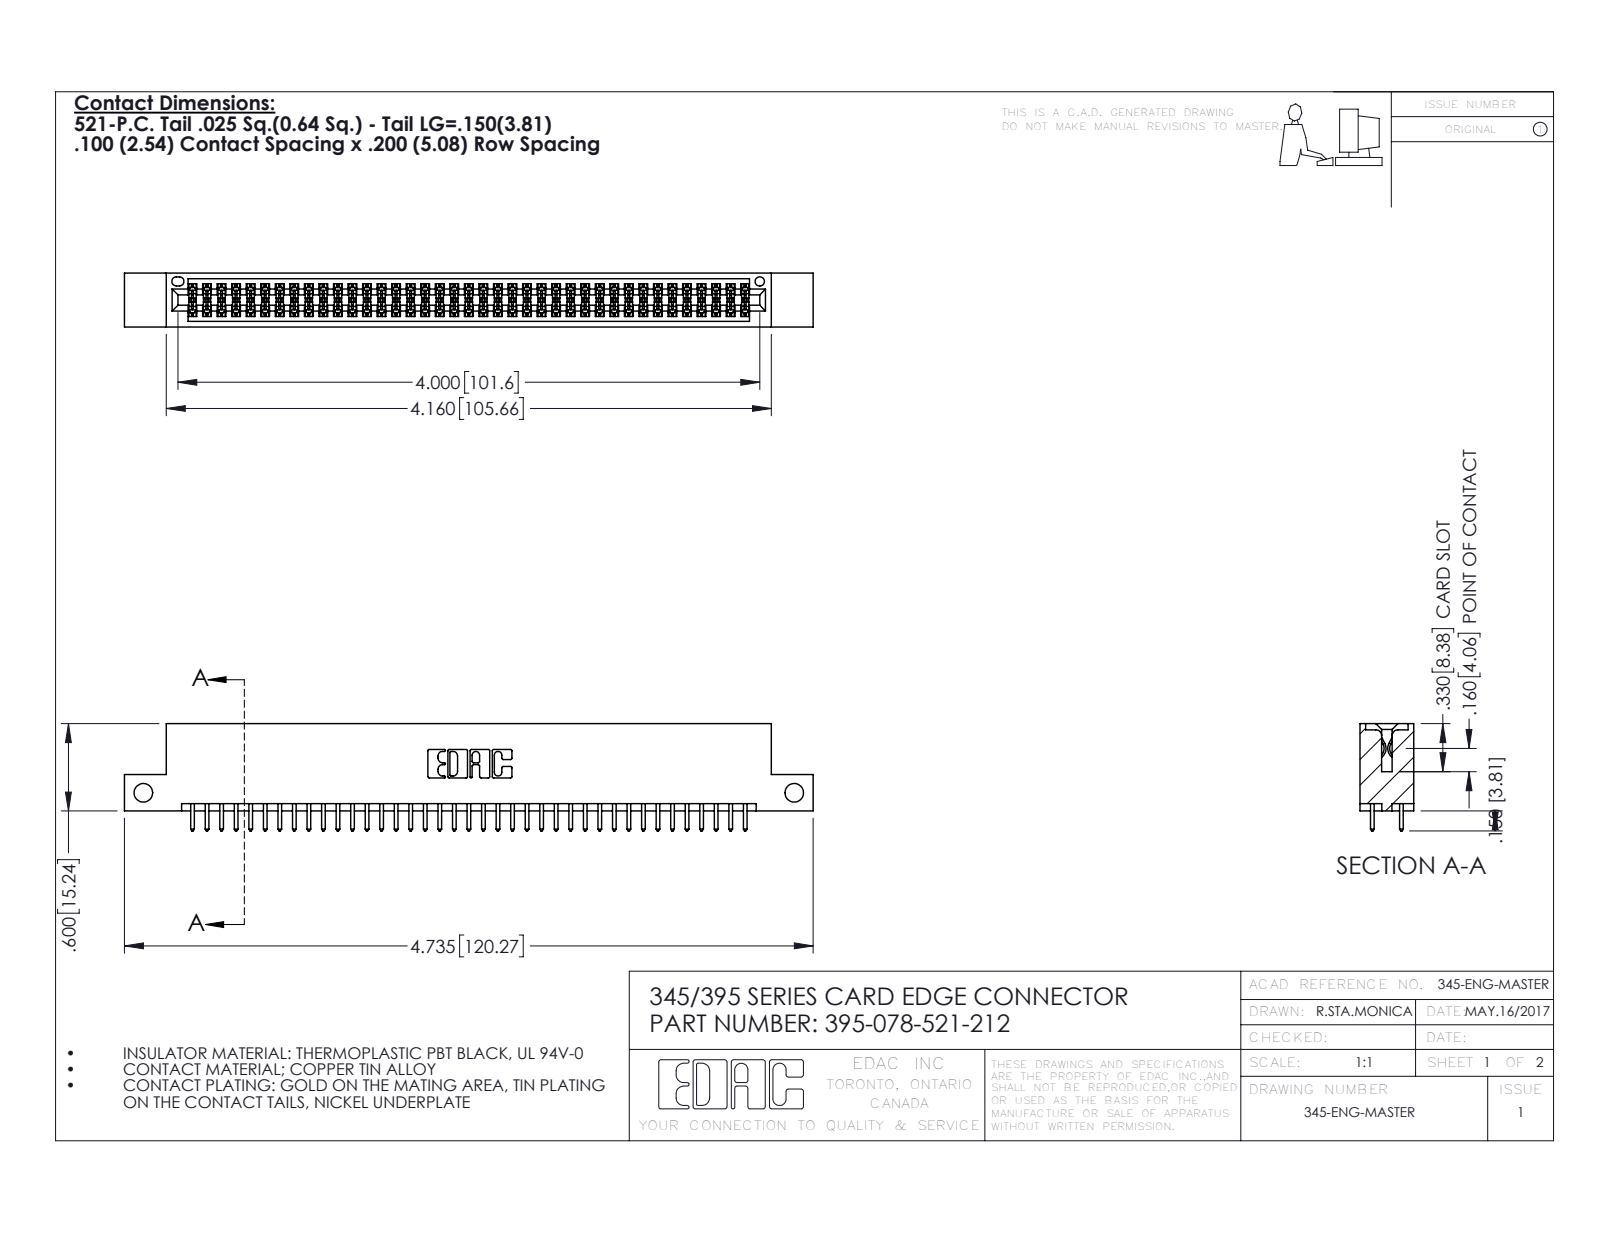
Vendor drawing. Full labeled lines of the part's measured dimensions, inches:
Part name (STEP PRODUCT): 345 Part_Flush Mounting Lugs - Side Mount; 395-078-521-212; 345-292-001_345-293-121
STEP written by: SolidWorks 2016 (CONFIG_CONTROL_DESIGN)
Units: inches
Bodies: 79 solids, 4026 faces (2654 planar, 1372 cylindrical, 0 other)
Overall size (bounding box): 4.735 × 0.737 × 0.37
Volume: 0.704 in³ · Surface area: 25.81 in²
Round holes (diameter × count): ⌀0.128 ×2, ⌀0.064 ×1
Partial cylindrical surfaces — rounded edges, fillets, slot ends (radius × count): R0.006 ×117, R0.01 ×78, R0.01 ×22, R0.007 ×6, R0.031 ×6, R0.026 ×3, R0.014 ×2, R0.019 ×2
Main face-to-face distances: 0.298, 0.072, 0.2, 0.37, 0.098, 0.272, 0.025, 0.225, 0.175, 0.149
Hole centre spacings: 4.475
